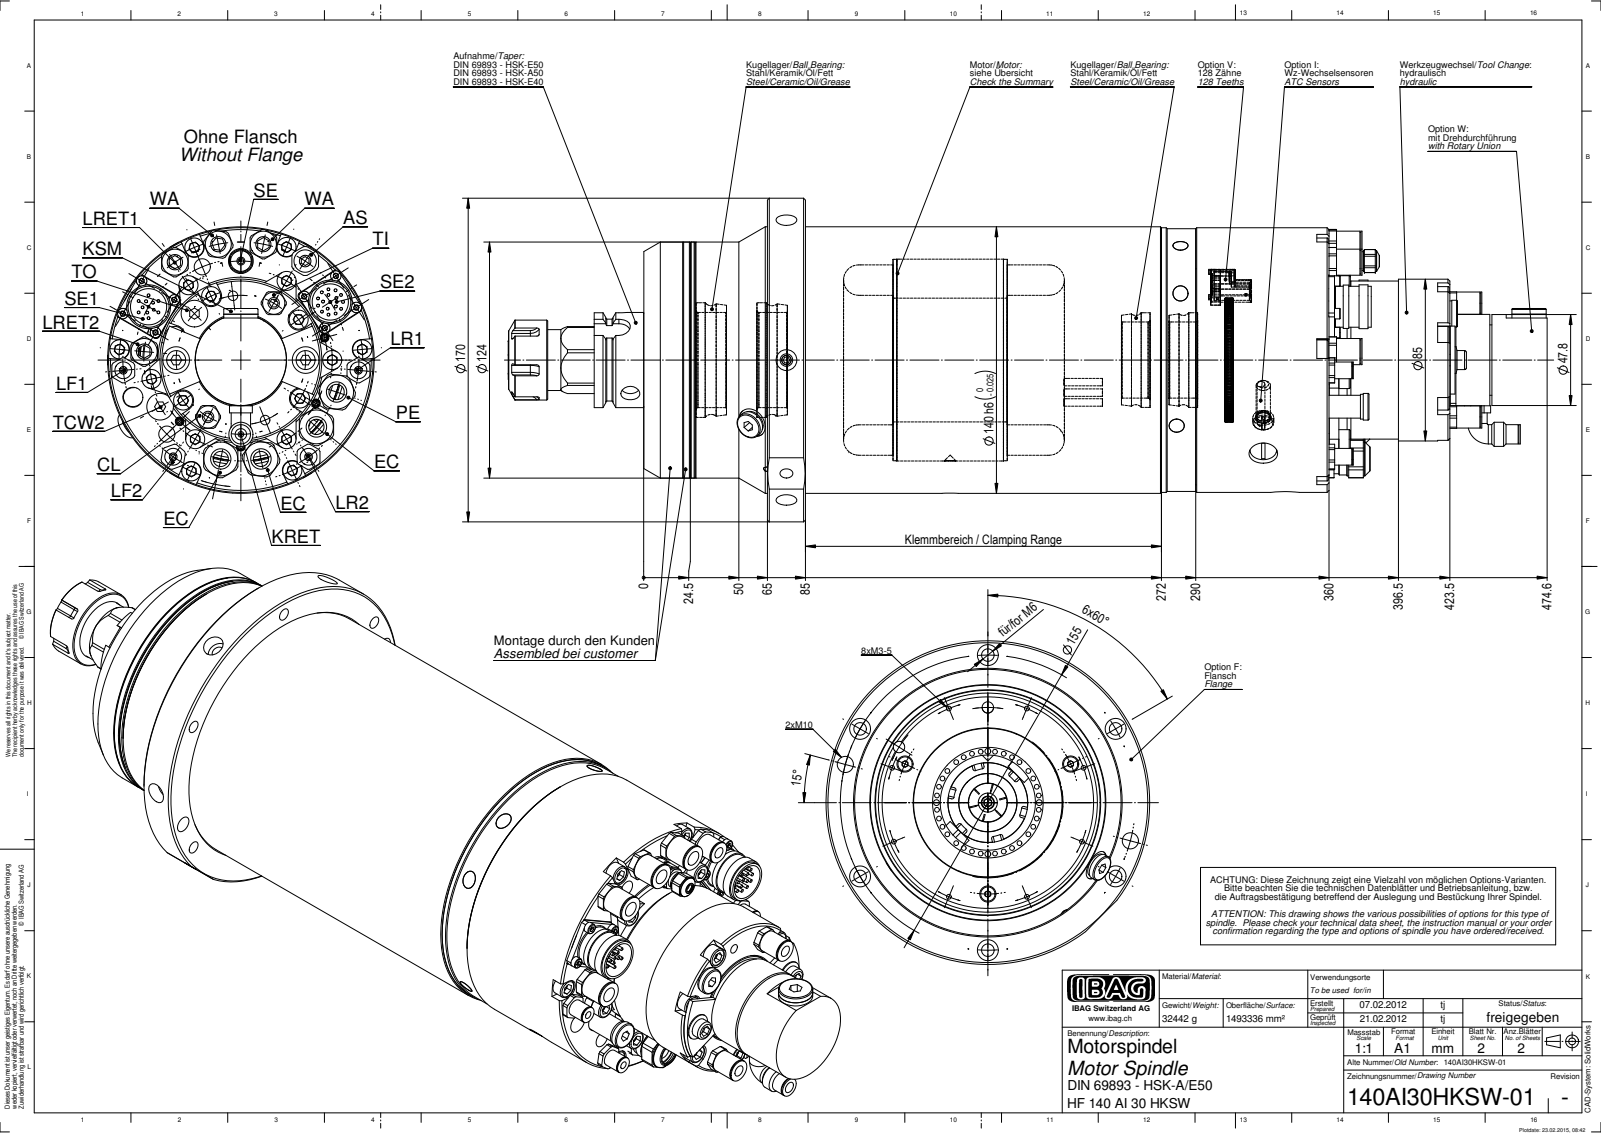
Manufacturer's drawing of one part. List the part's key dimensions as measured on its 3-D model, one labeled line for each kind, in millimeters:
Part name (STEP PRODUCT): 140AI30HKSW-01
STEP written by: SolidWorks 2010 (CONFIG_CONTROL_DESIGN)
Units: millimetres
Bodies: 0 solids, 1598 faces (617 planar, 713 cylindrical, 268 other)
Overall size (bounding box): 478.7 × 170 × 170
Round holes (diameter × count): ⌀2.5 ×44, ⌀8 ×9, ⌀11 ×9, ⌀6.6 ×8, ⌀6 ×6, ⌀8.5 ×5, ⌀3.1 ×4, ⌀4 ×4, ⌀10.7 ×4, ⌀15 ×4, ⌀16.2 ×4, ⌀5 ×3
Round bosses / shafts (diameter × count): ⌀1.5 ×28, ⌀10 ×20, ⌀5.5 ×9, ⌀14 ×6, ⌀17.8 ×4, ⌀16.79 ×4, ⌀15.59 ×4, ⌀13.7 ×4
Partial cylindrical surfaces — rounded edges, fillets, slot ends (radius × count): R5.2 ×6, R5.5 ×6, R6.6 ×6, R7.75 ×4, R9.9 ×4, R6.05 ×1, R7.6 ×1
Main face-to-face distances: 187, 275, 88, 20, 207, 295, 68.8, 48.8, 255.8, 343.8
Hole centre spacings: 4.7, 9.38, 20.23, 38.19, 53.8, 21.1, 30.97, 34.72
